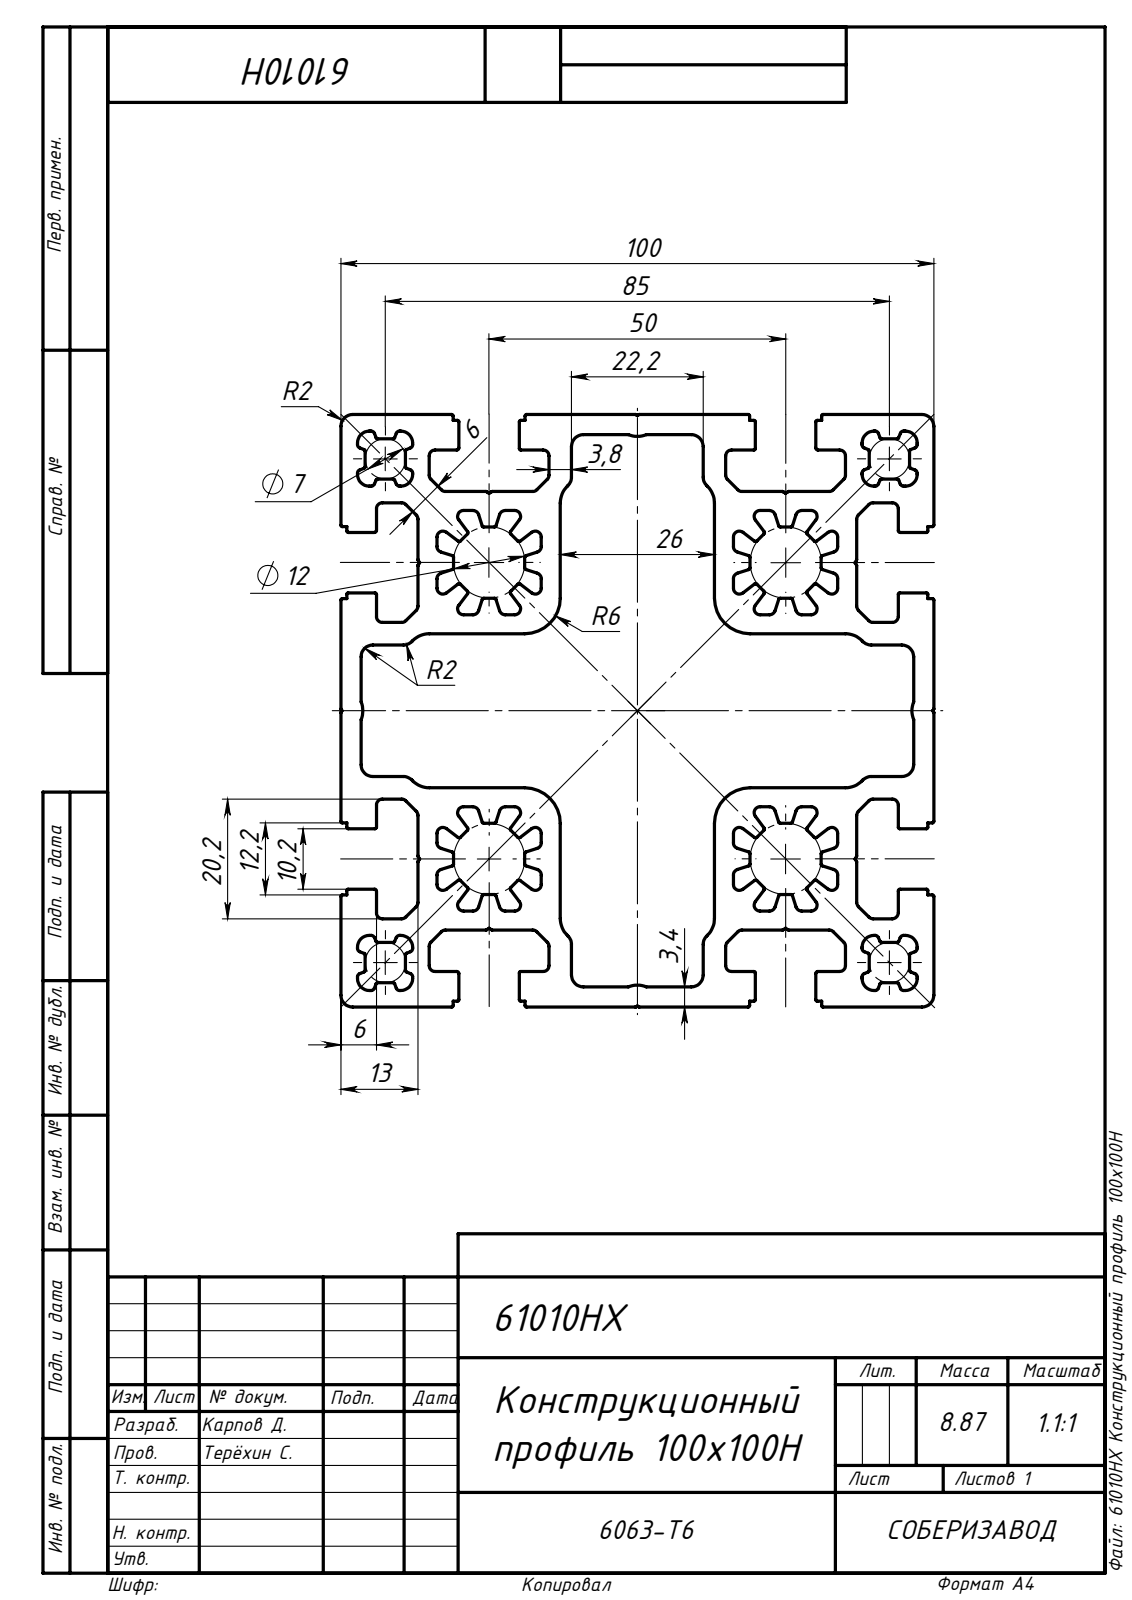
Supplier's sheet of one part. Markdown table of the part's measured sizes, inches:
| quantity | value |
| --- | --- |
| STEP written by | SolidWorks 2019 (AUTOMOTIVE_DESIGN) |
| units | inches |
| bodies | 1 solid, 774 faces (394 planar, 380 cylindrical, 0 other) |
| overall size | 39.37 × 3.937 × 3.937 |
| volume | 200.5 in³ |
| surface area | 2 520 in² |
| partial cylindrical surfaces (radius × count) | 0.01 × 112, 0.039 × 112, 0.012 × 48, 0.079 × 36, 0.024 × 32, 0.157 × 12, 0.014 × 8, 0.236 × 4 |
| main face-to-face distances | 1.969, 3.937, 0.945, 1.457, 2.48, 0.512, 3.425, 1.22, 0.075, 1.024 |
